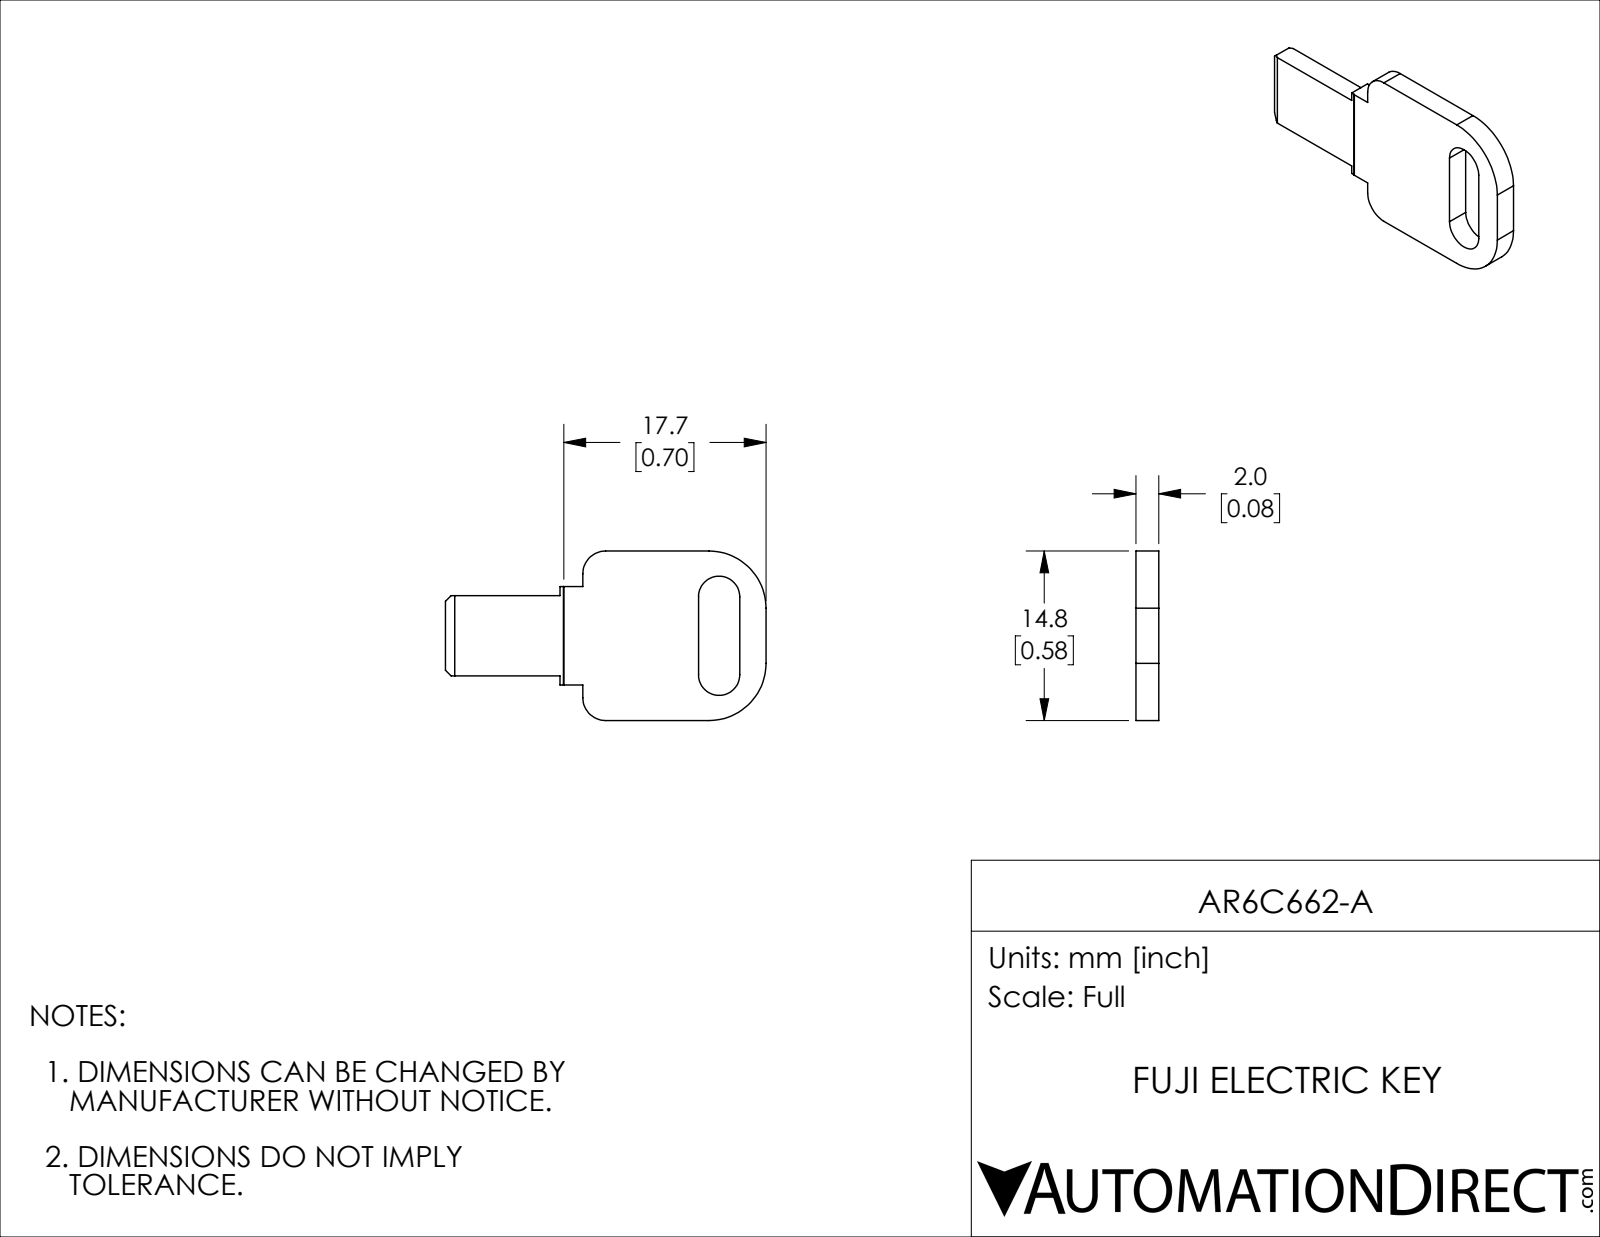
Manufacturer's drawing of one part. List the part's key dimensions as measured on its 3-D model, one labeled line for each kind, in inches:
Part name (STEP PRODUCT): AR6C662-A
STEP written by: SolidWorks 2021 (CONFIG_CONTROL_DESIGN)
Units: inches
Bodies: 1 solid, 30 faces (24 planar, 6 cylindrical, 0 other)
Overall size (bounding box): 1.102 × 0.583 × 0.079
Volume: 0.033 in³ · Surface area: 1.17 in²
Partial cylindrical surfaces — rounded edges, fillets, slot ends (radius × count): R0.071 ×2, R0.079 ×2, R0.197 ×2
Main face-to-face distances: 0.079, 0.078, 0.077, 0.154, 0.429, 0.276, 0.583, 0.142, 0.232, 0.091
